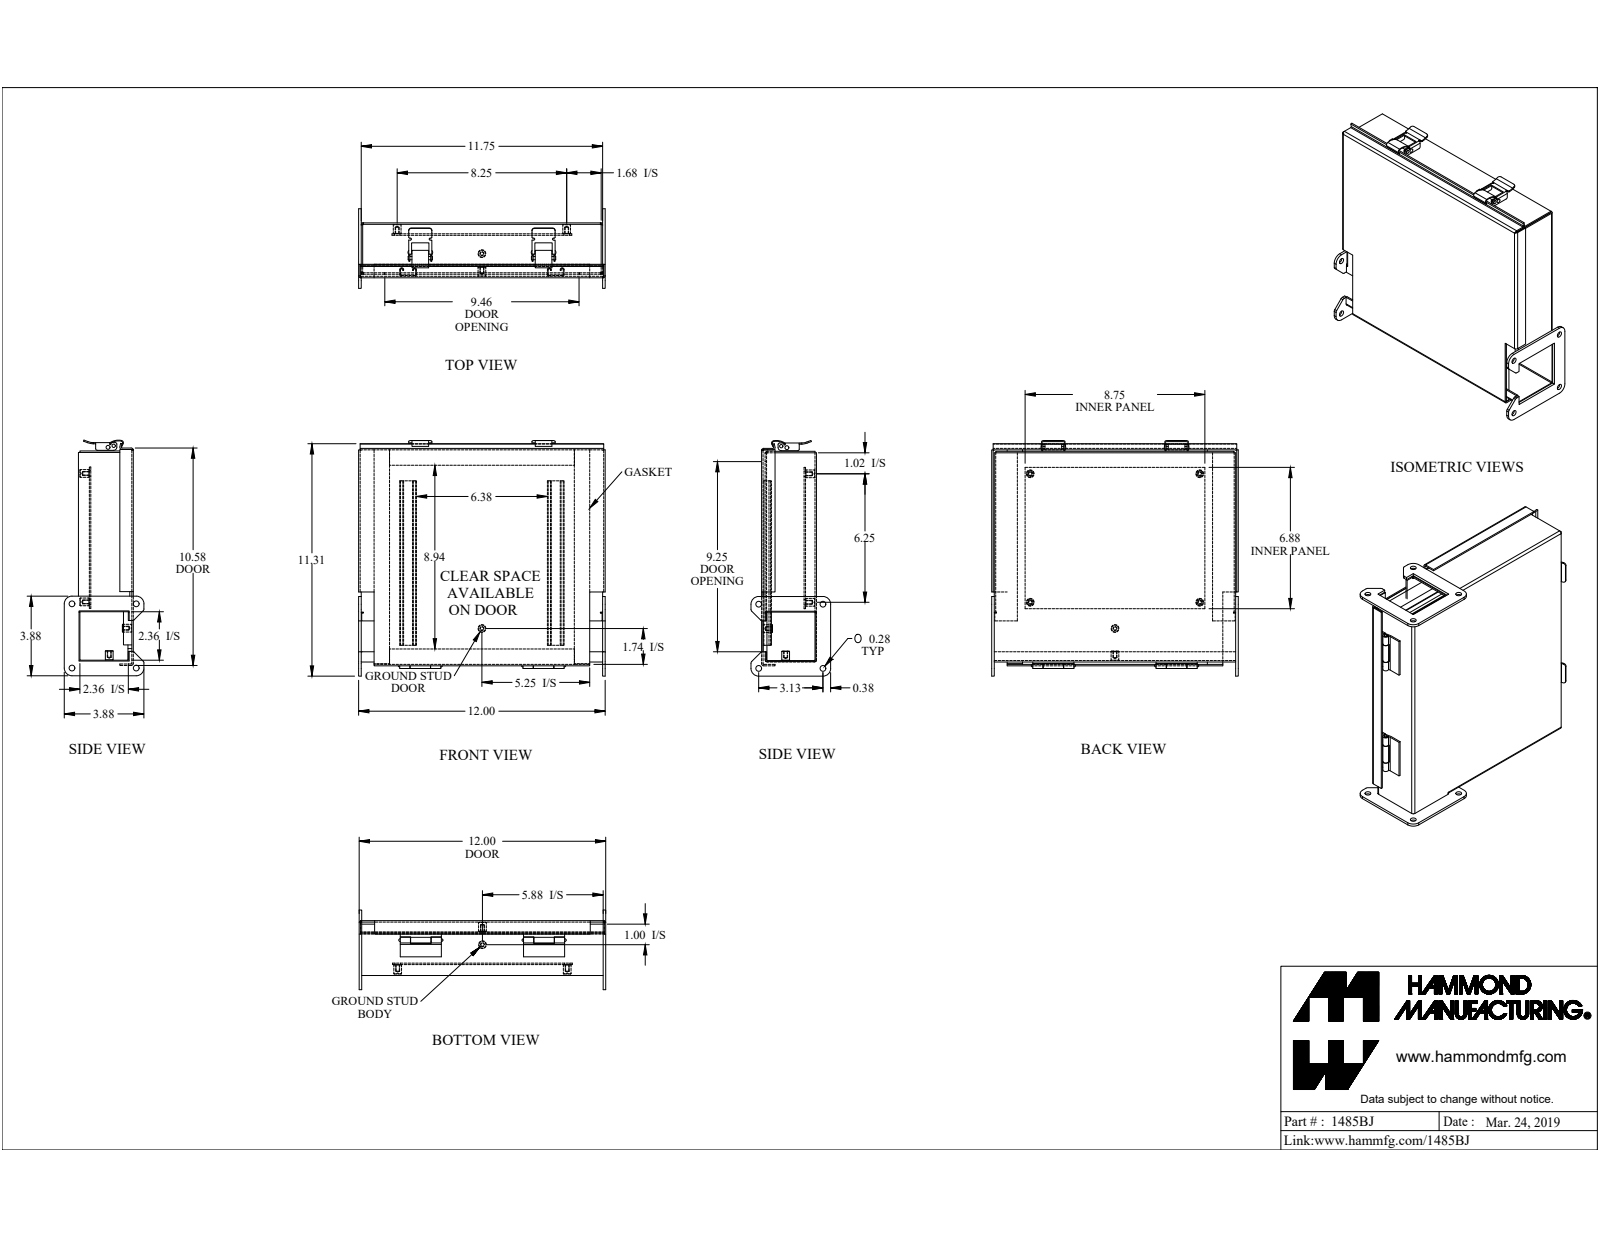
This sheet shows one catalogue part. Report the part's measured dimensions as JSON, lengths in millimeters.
{"part_name": "1485BJ", "step_written_by": "SolidWorks 2019 (CONFIG_CONTROL_DESIGN)", "units": "millimeters", "bodies": {"solids": 30, "faces": 550, "planar": 332, "cylindrical": 188, "other": 30}, "overall_size": [304.8, 291.2, 98.4], "volume_mm3": 681200, "surface_area_mm2": 716800, "round_holes": [[4, 6], [6.7, 4], [7.1, 4], [3.2, 1], [4.2, 1]], "round_bosses_or_shafts": [[9.5, 6], [7, 1], [4.1, 1], [4, 1], [3.2, 1], [3.2, 1]], "partial_cylinders_radius": [[0.9, 12], [1.1, 12], [2.1, 12], [2.7, 12], [3.2, 9], [0.7, 8], [2.2, 8], [0.4, 4]], "face_to_face_distances": [1.8, 66, 13.5, 52.5, 64.2, 67.9, 11.7, 54.4, 15.3, 50.7], "hole_center_spacings": [79.4, 158.8, 262.9, 109.7, 112.2, 209.6, 209.6, 218]}
